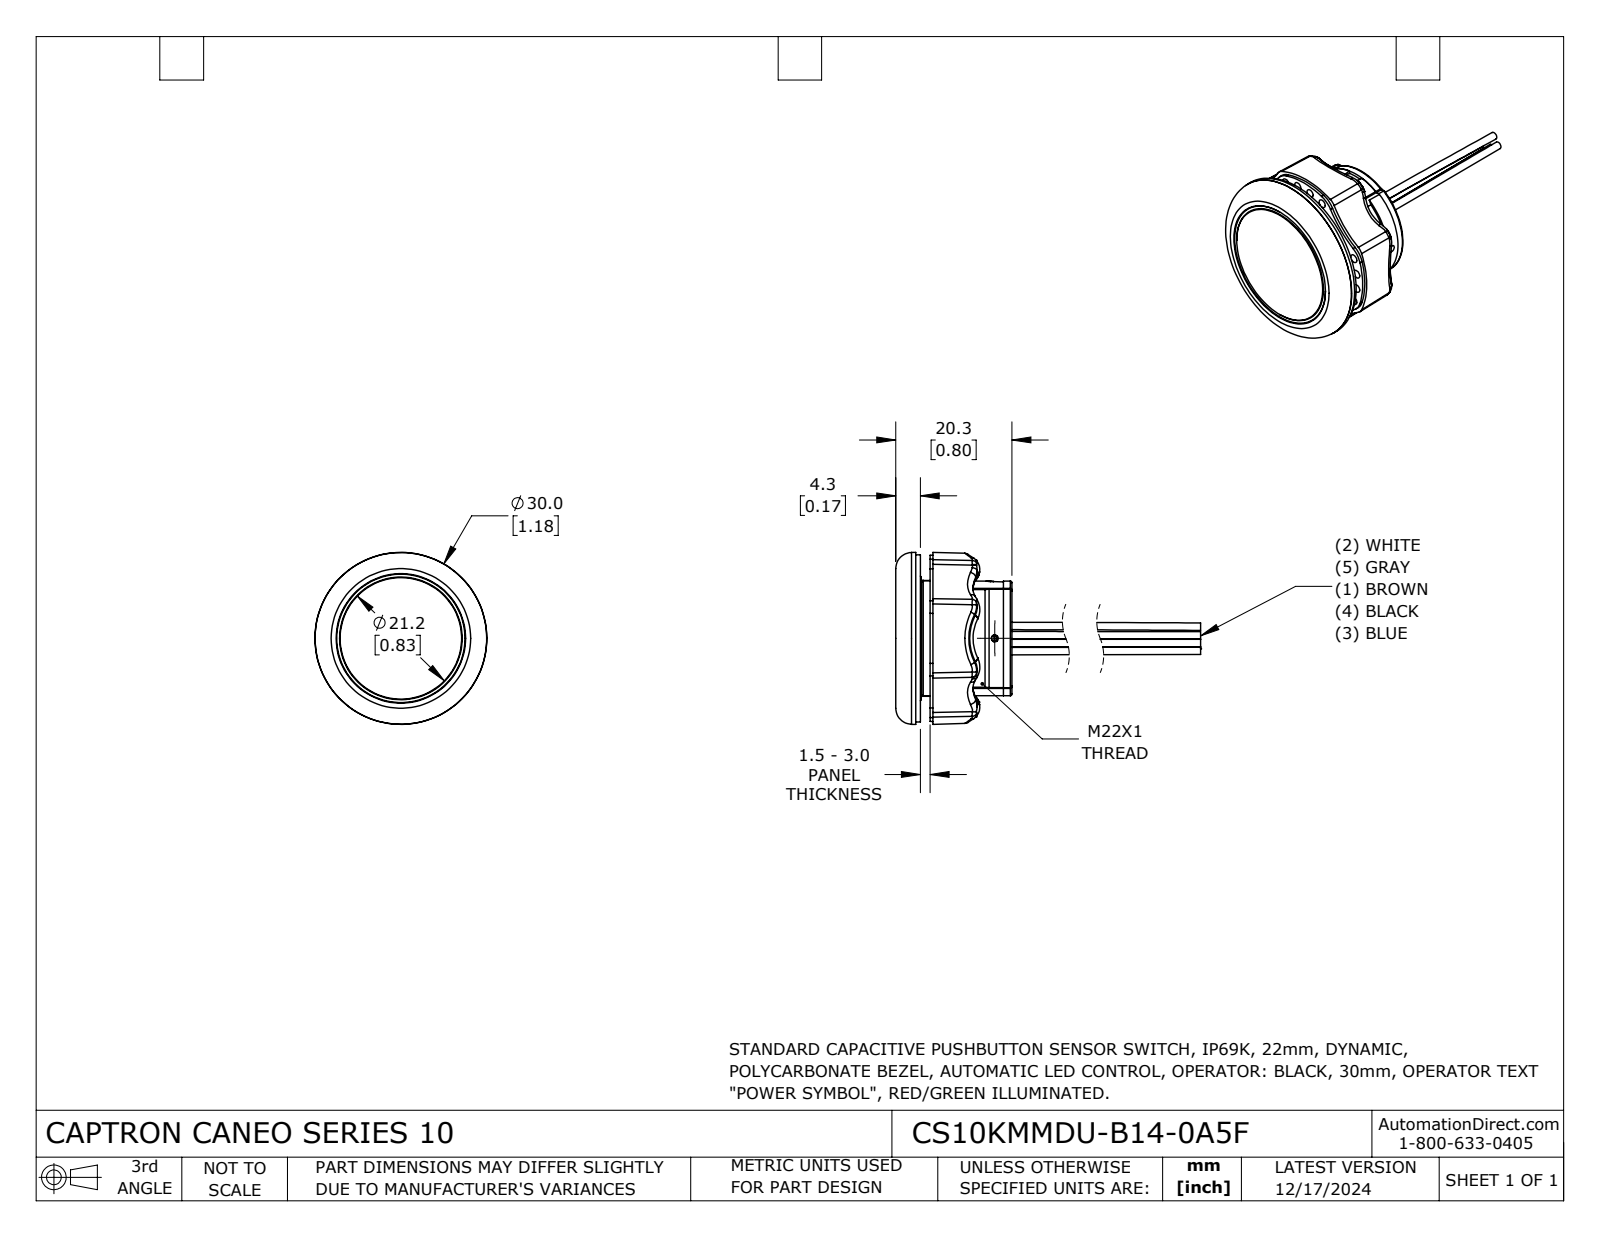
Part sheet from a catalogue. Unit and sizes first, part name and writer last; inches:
Units: inches
Overall size (bounding box): 2.049 × 1.181 × 1.181
Round holes (diameter × count): ⌀0.047 ×1, ⌀0.827 ×1, ⌀0.927 ×1
Round bosses / shafts (diameter × count): ⌀1.181 ×1, ⌀1.15 ×1, ⌀0.72 ×1, ⌀0.717 ×1
Partial cylindrical surfaces — rounded edges, fillets, slot ends (radius × count): R0.012 ×8, R0.004 ×6, R0.01 ×6, R0.295 ×6, R0.02 ×4, R0.039 ×4, R0.689 ×4, R0.362 ×1
Main face-to-face distances: 0.169, 0.63, 0.799, 0.067, 0.563, 0.236, 0.079, 0.551, 0.248, 0.242
Volume: 0.649 in³ · Surface area: 9.995 in²
Bodies: 7 solids, 601 faces (204 planar, 75 cylindrical, 322 other)
Part name (STEP PRODUCT): CS10KMMDU-B14-0A5F
STEP written by: SolidWorks 2024 (CONFIG_CONTROL_DESIGN)
